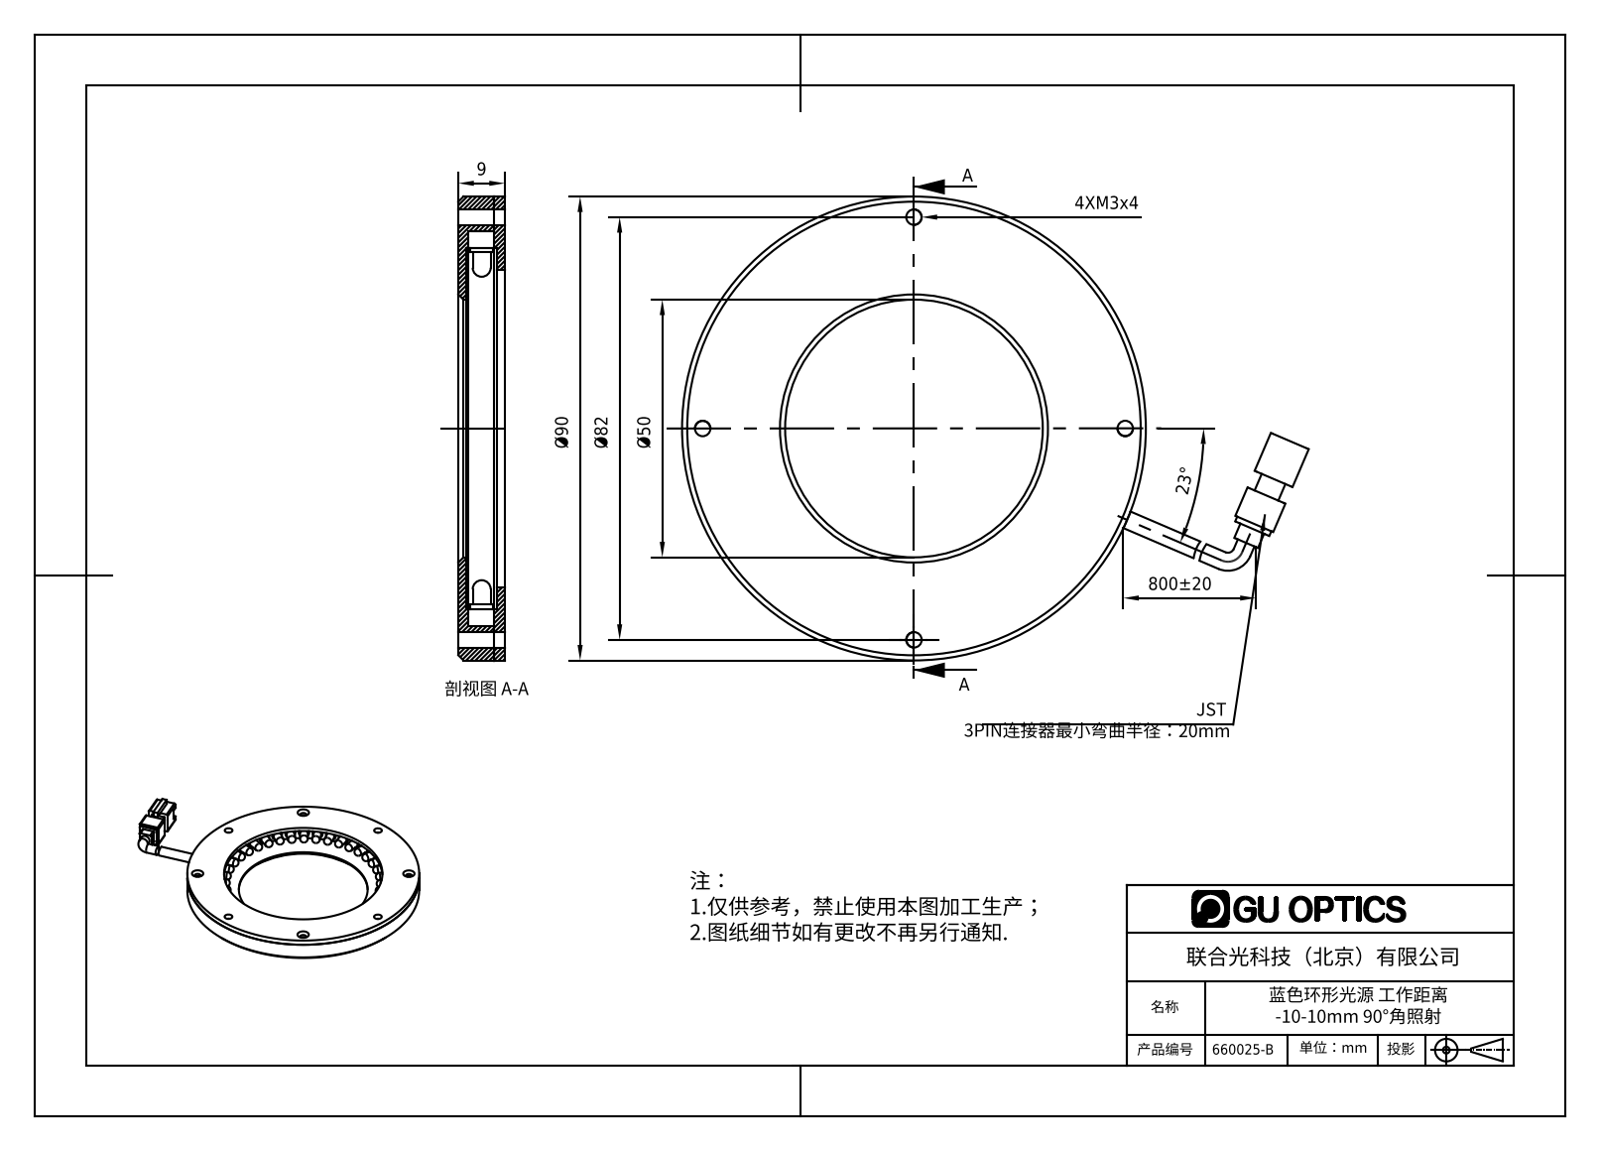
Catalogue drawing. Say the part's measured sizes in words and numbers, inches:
The part is named "660025-B". Its 3-D file was written by "SolidWorks 2016 (AUTOMOTIVE_DESIGN)". It is 45 solids with 884 faces: 553 planar, 267 cylindrical and 64 other. Overall it measures 4.788 by 3.543 by 0.394 inches. Its volume is 1.544 cubic inches and its surface area 43.47 square inches. Round holes: 8 of diameter 0.118, 4 of diameter 0.063, 4 of diameter 0.079, 4 of diameter 0.094, 2 of diameter 0.138, 1 of diameter 1.969, 1 of diameter 2.42, 1 of diameter 2.717, 1 of diameter 2.756, 1 of diameter 3.019. Round bosses or shafts: 40 of diameter 0.15, 40 of diameter 0.118, 2 of diameter 0.138, 1 of diameter 3.543, 1 of diameter 2.732. Partial cylindrical surfaces (rounded edges, fillets, slot ends): 8 of radius 0.02, 4 of radius 0.039, 2 of radius 0.071, 1 of radius 0.197, 1 of radius 1.319, 1 of radius 1.461. The main face-to-face distances are 0.276, 0.079, 0.354, 0.059, 0.217, 0.295, 0.02, 0.236, 0.197, 0.039. The hole center spacings are 2.983, 3.228, 1.235, 1.614, 2.283, 1.234, 1.237, 2.282.
